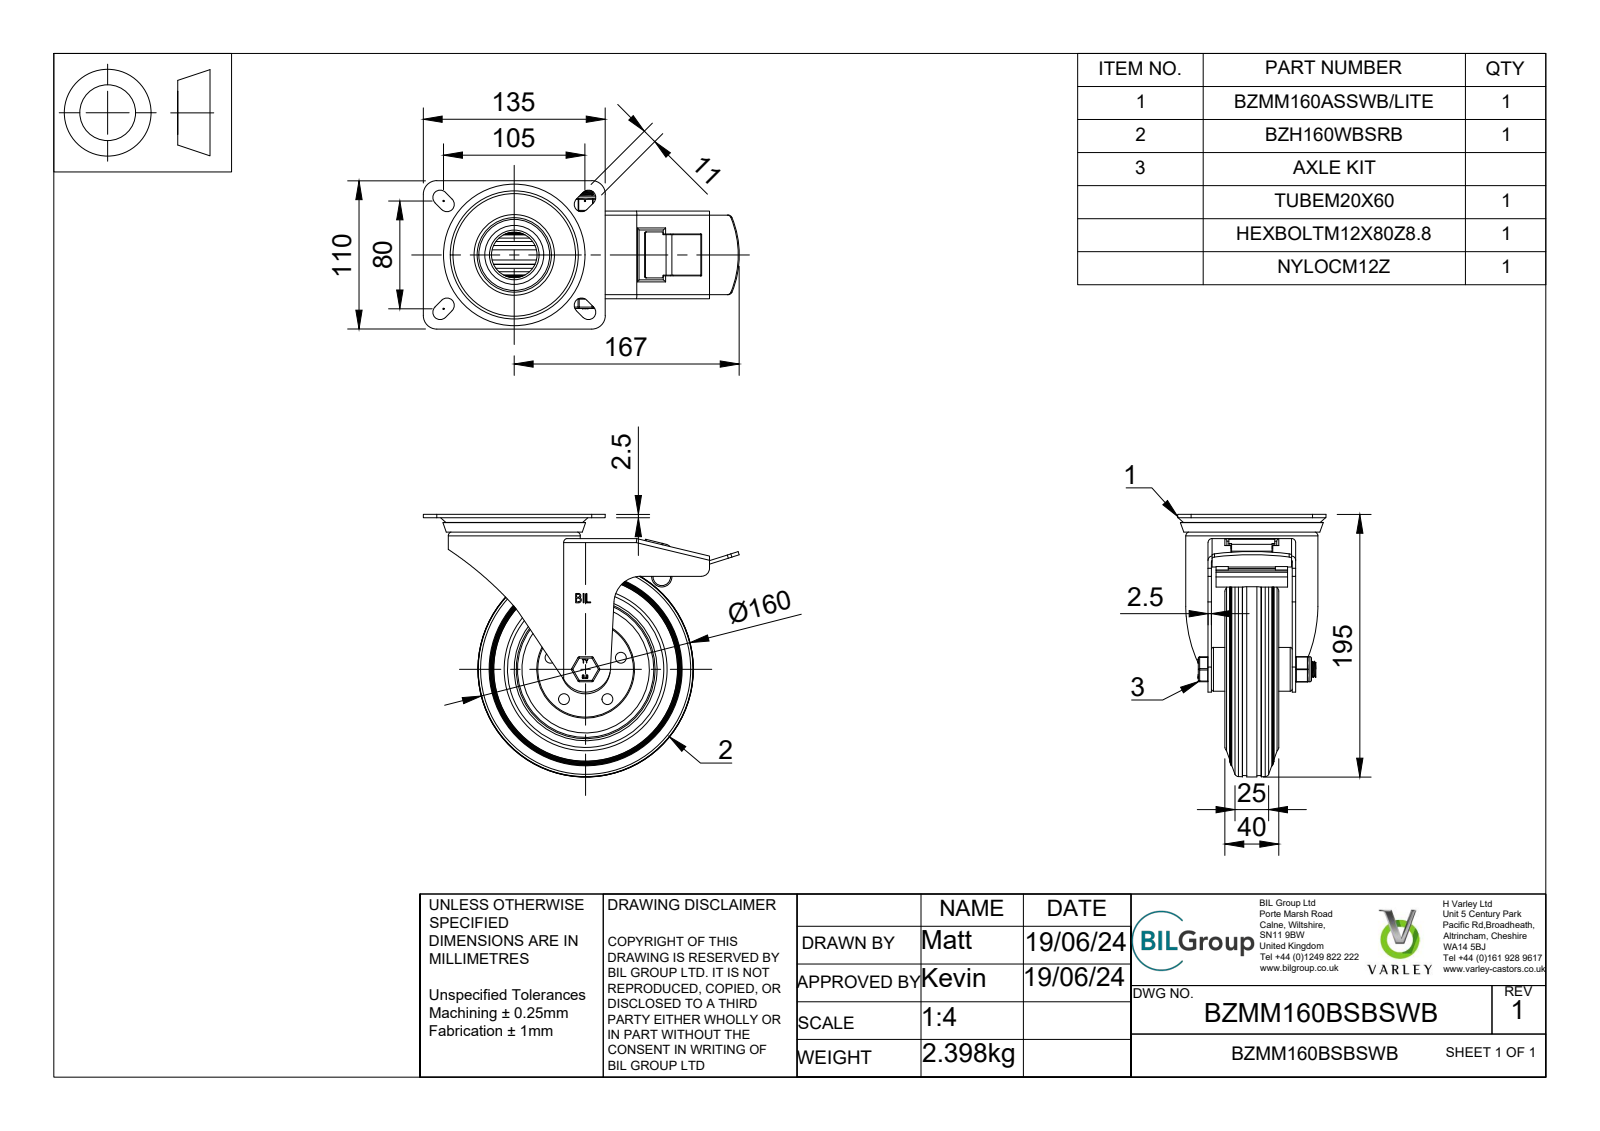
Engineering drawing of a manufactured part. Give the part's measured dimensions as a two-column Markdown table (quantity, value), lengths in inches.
| quantity | value |
| --- | --- |
| part name | BZMM160BSBSWB v3; BZMM150ASSWBLITE v1; ZINC PLATED, PRESSED STEEL TOP PLATE; ZINC PLATED, PRESSED STEEL TOP PLATE Geometry (+7 more) |
| STEP written by | Autodesk Translation Framework v13.14.0.145 (AUTOMOTIVE_DESIGN) |
| units | inches |
| bodies | 68 solids, 744 faces (329 planar, 217 cylindrical, 198 other) |
| overall size | 9.232 × 7.677 × 4.331 |
| volume | 44.17 in³ |
| surface area | 433.1 in² |
| round holes (diameter × count) | 0.236 × 5, 0.472 × 1, 0.48 × 1, 0.492 × 1, 0.551 × 1, 0.787 × 1, 1.161 × 1, 1.329 × 1, 1.565 × 1, 3.661 × 1 |
| round bosses / shafts (diameter × count) | 0.177 × 10, 0.315 × 5, 4.055 × 1, 3.858 × 1, 3.071 × 1, 1.969 × 1, 1.28 × 1, 0.783 × 1 |
| partial cylindrical surfaces (radius × count) | 0.02 × 19, 0.039 × 13, 0.059 × 12, 0.217 × 8, 0.118 × 7, 0.03 × 6, 0.079 × 4, 0.394 × 4 |
| main face-to-face distances | 0.098, 0.709, 0.079, 0.157, 1.181, 0.354, 1.28, 2.461, 0.197, 0.039 |
| hole center spacings | 1.272, 1.082, 2.057, 1.081, 2.058 |
